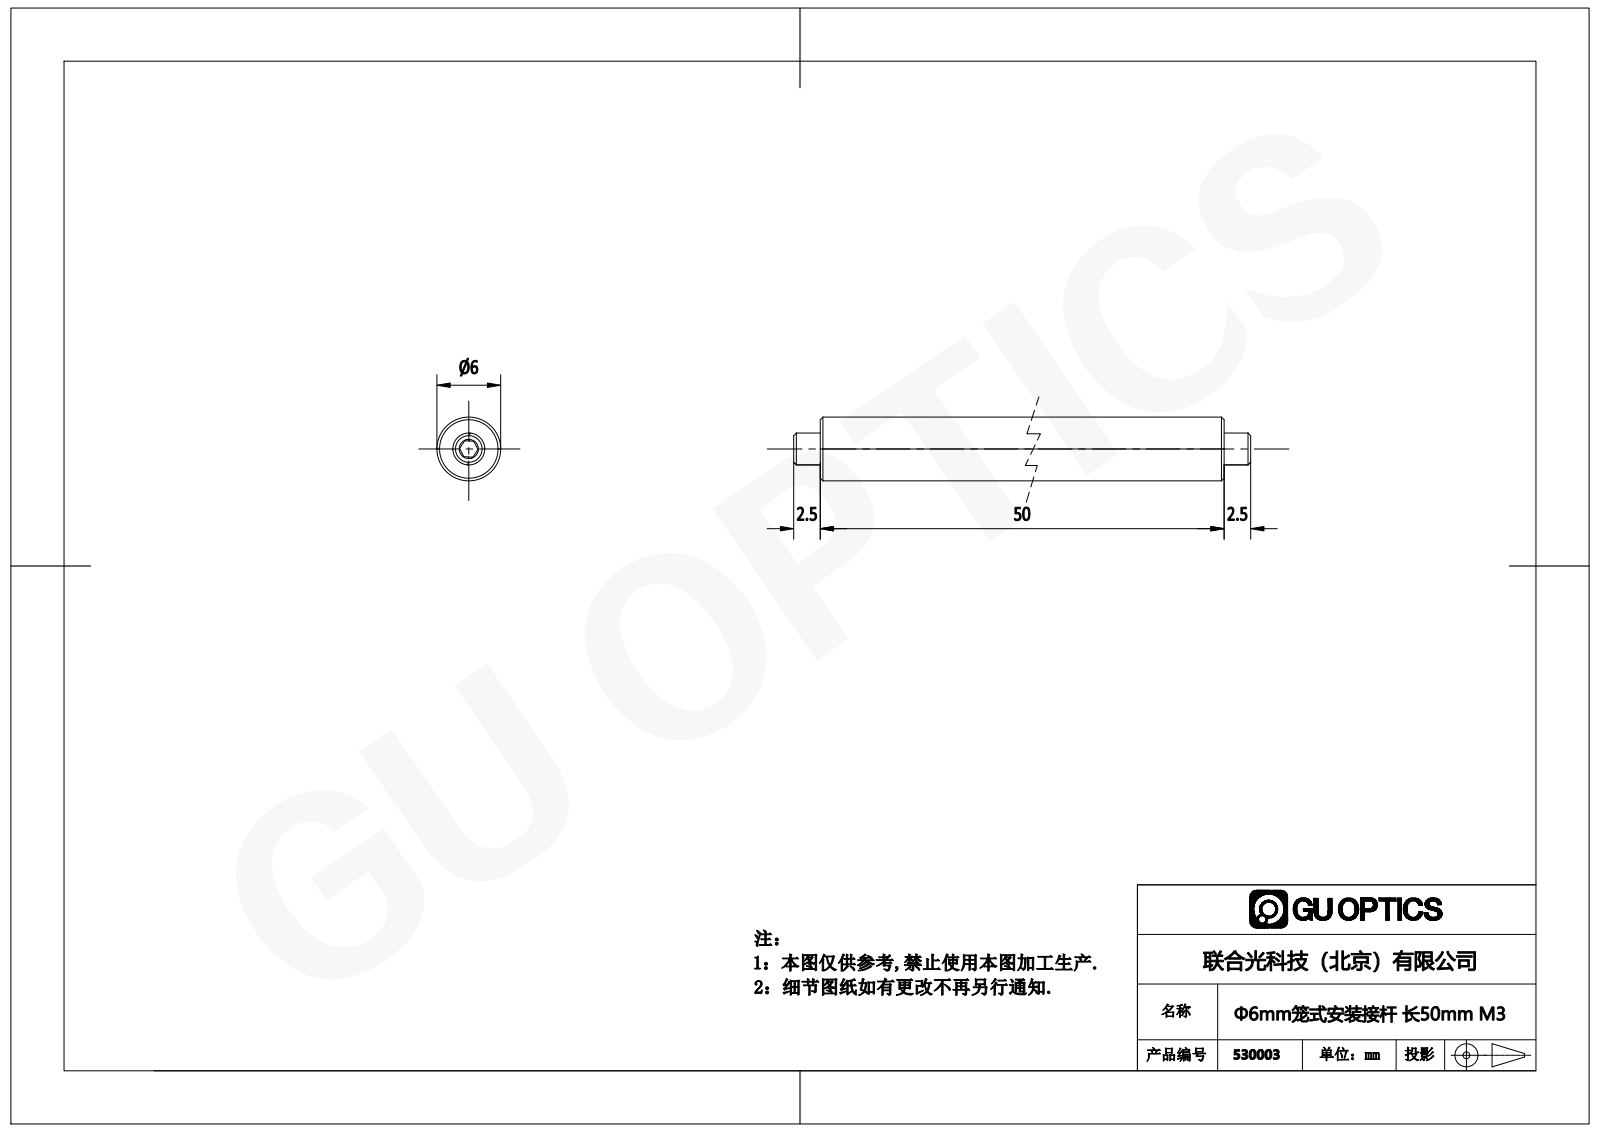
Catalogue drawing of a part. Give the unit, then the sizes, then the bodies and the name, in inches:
Units: inches
Overall size (bounding box): 2.165 × 0.236 × 0.236
Round bosses / shafts (diameter × count): ⌀0.236 ×1, ⌀0.118 ×1
Main face-to-face distances: 1.969, 0.059, 0.098, 2.067, 0.039, 2.126, 2.028, 2.165, 2.087
Bodies: 0 solids, 36 faces (18 planar, 6 cylindrical, 12 other)
STEP written by: SolidWorks 2018 (AUTOMOTIVE_DESIGN)
